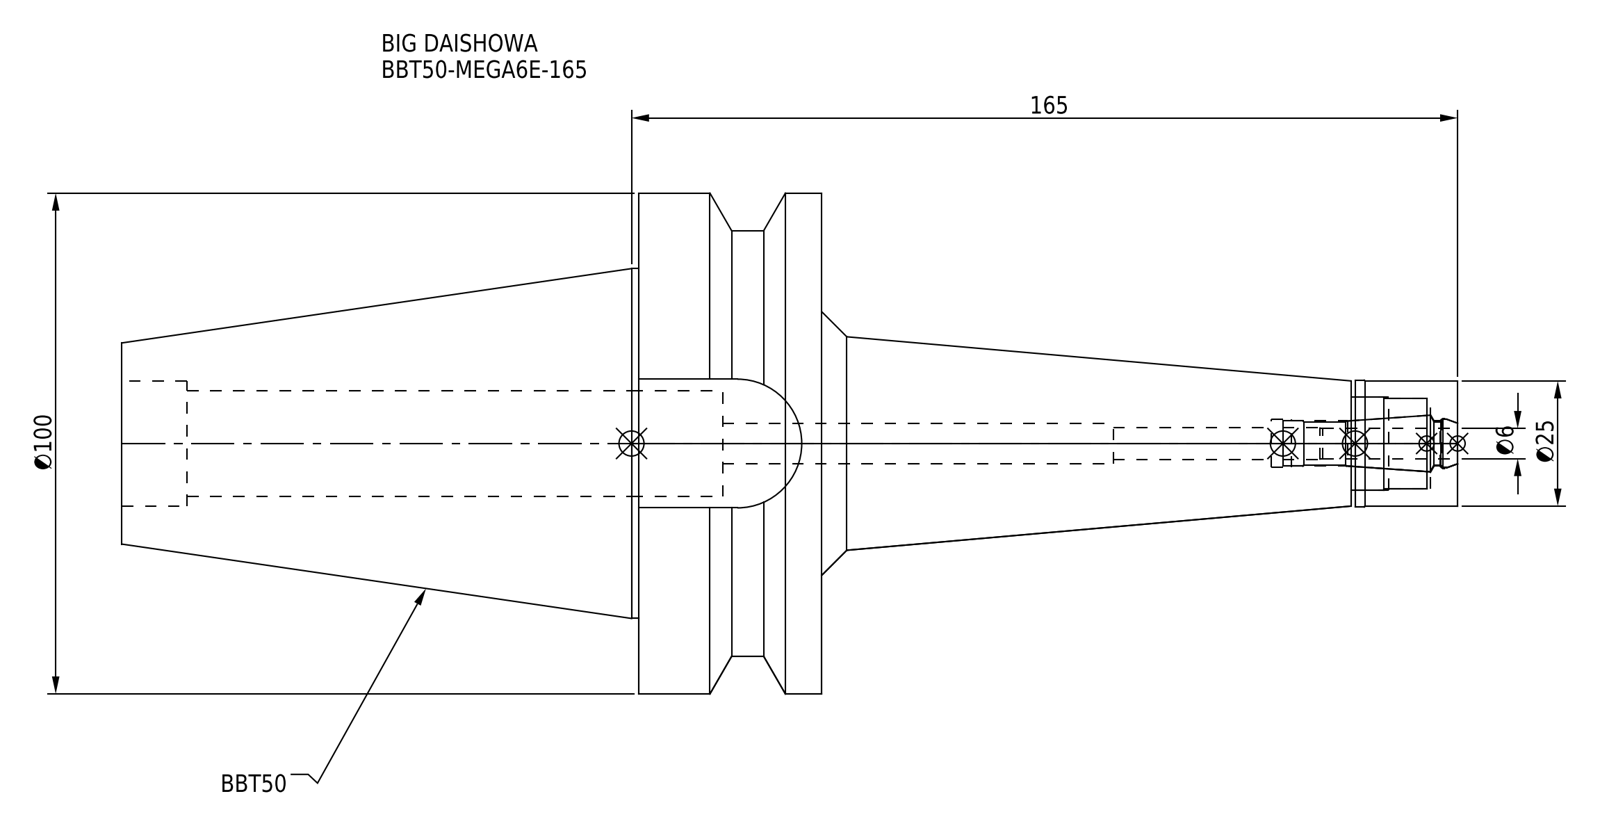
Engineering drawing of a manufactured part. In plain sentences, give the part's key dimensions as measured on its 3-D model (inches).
The part is named "BBT50-MEGA6E-165-060.stp; BBT50-MEGA6E-165; DXF_TEMP_ASSY_ASM_4_ASM.stp; BBT50ME06165-060_ASM.stp (+3 more)". Its 3-D file was written by "SolidWorks 2019 (CONFIG_CONTROL_DESIGN)". It is 2 solids with 81 faces: 21 planar, 40 cylindrical and 20 other. Overall it measures 10.504 by 3.937 by 3.937 inches. Its volume is 34.1 cubic inches and its surface area 110.7 square inches. Round holes: 1 of diameter 0.252, 1 of diameter 0.315, 1 of diameter 0.354, 1 of diameter 0.378, 1 of diameter 0.39, 1 of diameter 0.709, 1 of diameter 0.728, 1 of diameter 0.835, 1 of diameter 0.984. Round bosses or shafts: 1 of diameter 3.937, 1 of diameter 3.346, 1 of diameter 2.75, 1 of diameter 0.996. Partial cylindrical surfaces (rounded edges, fillets, slot ends): 1 of radius 0.506. The main face-to-face distances are 1.437, 5.504, 4.067, 2.787, 1.012, 5, 6.437, 10.504, 0.657, 5.78.
